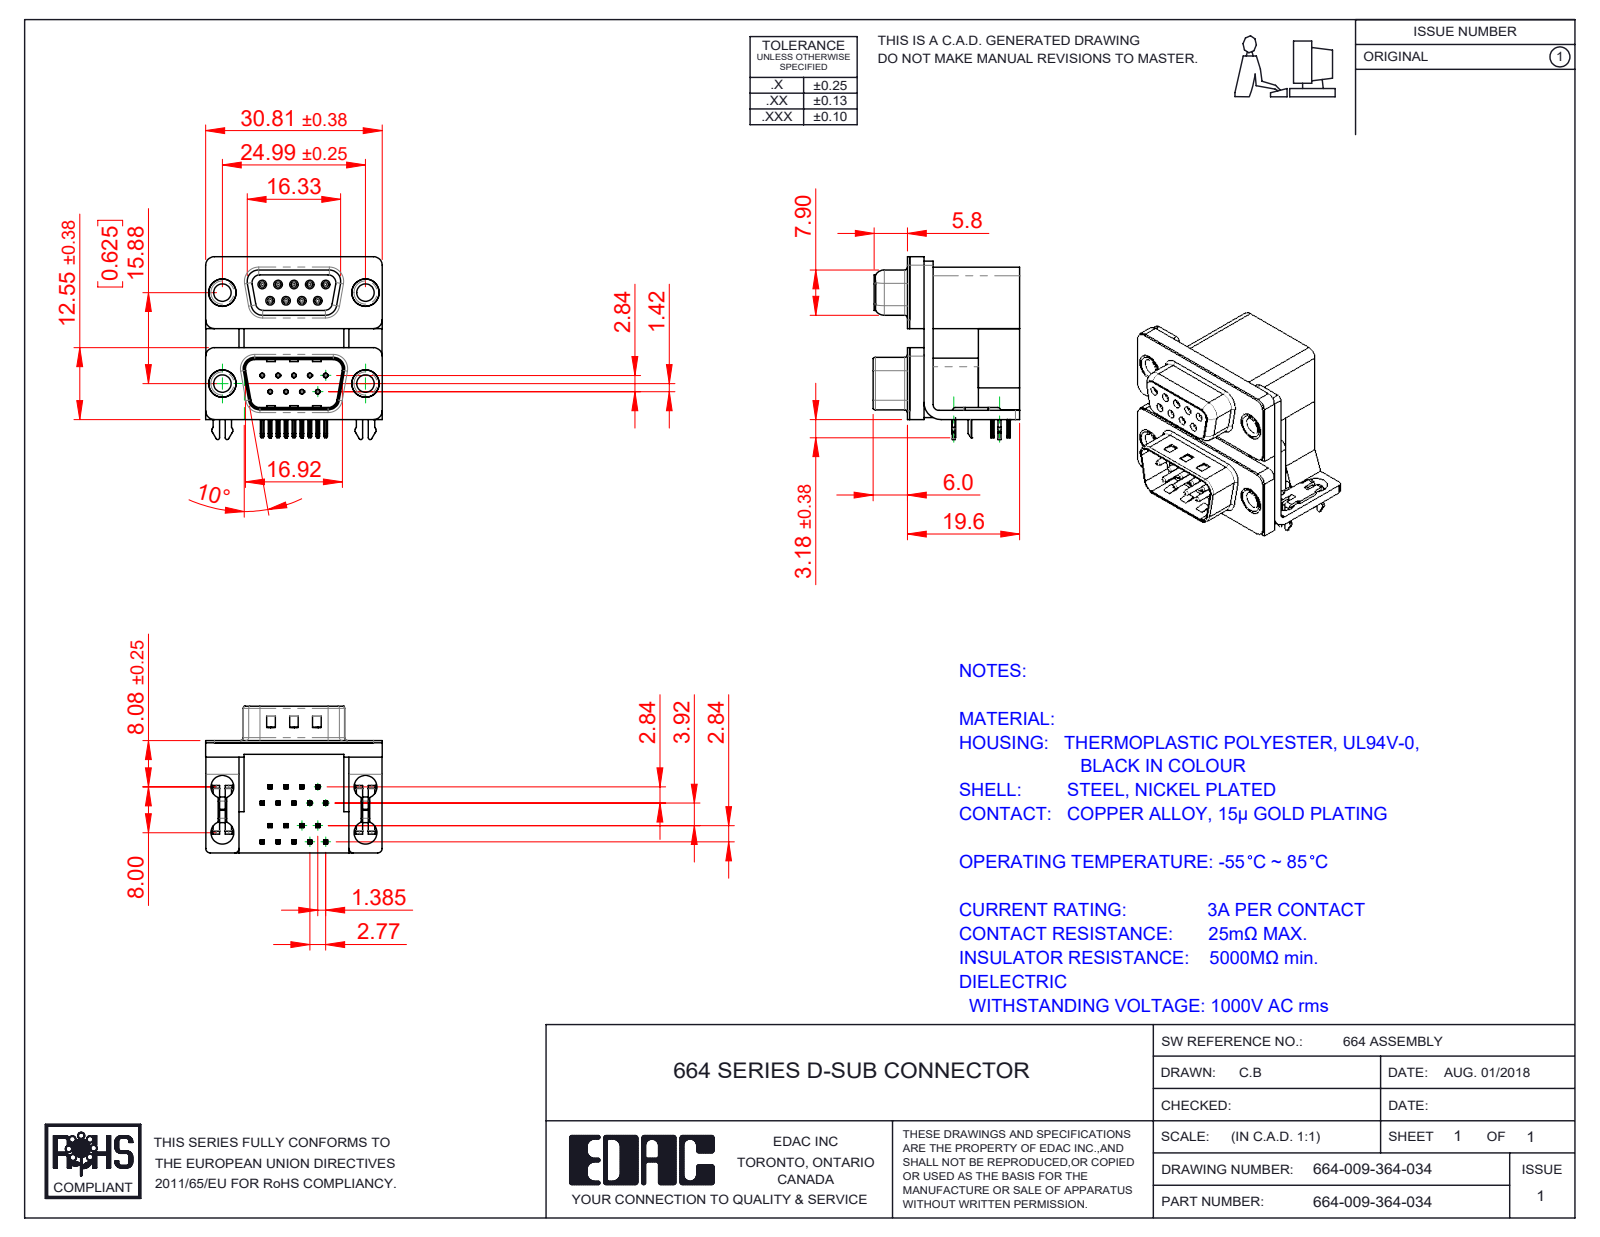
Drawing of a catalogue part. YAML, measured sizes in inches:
part_name: "664 Thru Hole Rivet; 664 Housing Upper_09 Contacts L; 664 Housing Lower_09 Contacts; 664 Shell Plug_09 Contacts (+8 more)"
step_written_by: "SolidWorks 2020 (CONFIG_CONTROL_DESIGN)"
units: inches
bodies: {solids: 31, faces: 2597, planar: 1365, cylindrical: 709, other: 523}
overall_size: [1.257, 1.213, 1.008]
volume: 0.629
surface_area: 19.11
round_holes:
  - {diameter: 0.031, count: 18}
  - {diameter: 0.014, count: 9}
  - {diameter: 0.035, count: 9}
  - {diameter: 0.157, count: 8}
  - {diameter: 0.12, count: 4}
  - {diameter: 0.138, count: 4}
  - {diameter: 0.189, count: 4}
  - {diameter: 0.197, count: 4}
round_bosses_or_shafts:
  - {diameter: 0.047, count: 9}
  - {diameter: 0.03, count: 9}
  - {diameter: 0.193, count: 4}
  - {diameter: 0.187, count: 4}
  - {diameter: 0.152, count: 4}
partial_cylinders:
  - {radius: 0.004, count: 74}
  - {radius: 0.01, count: 46}
  - {radius: 0.006, count: 36}
  - {radius: 0.005, count: 18}
  - {radius: 0.014, count: 18}
  - {radius: 0.02, count: 16}
  - {radius: 0.059, count: 13}
  - {radius: 0.03, count: 10}
face_to_face_distances: [0.016, 0.098, 0.657, 0.756, 0.772, 0.114, 0.283, 0.374, 0.472, 0.488]
hole_center_spacings: [0.124, 0.109, 0.635, 0.625, 0.218, 0.662, 0.516, 0.739]
